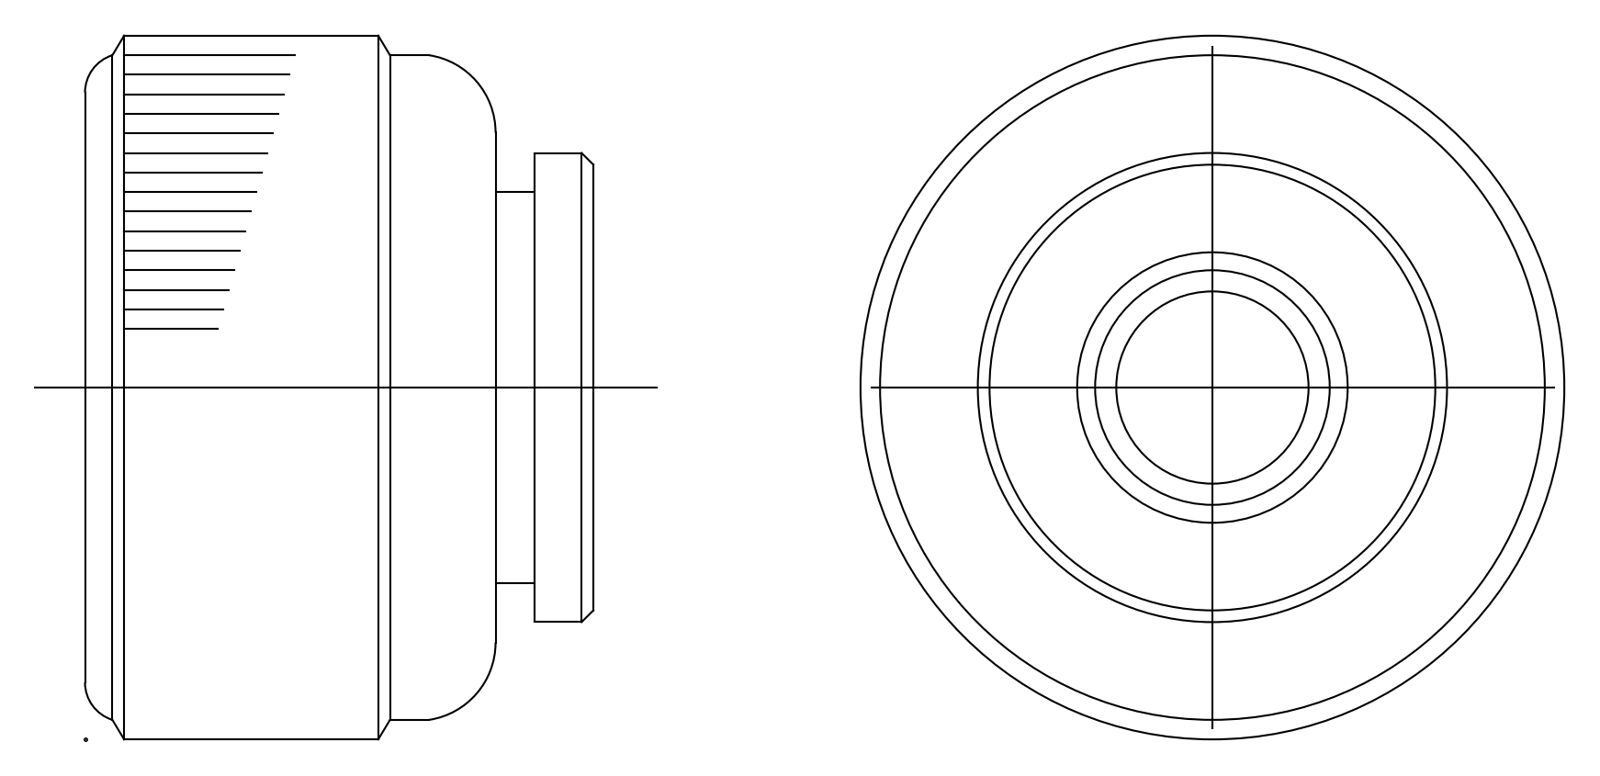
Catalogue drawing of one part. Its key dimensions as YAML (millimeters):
step_written_by: "spGate 20.6.3 (****-****-****-****) (AUTOMOTIVE_DESIGN)"
units: millimeters
bodies: {solids: 1, faces: 32, planar: 4, cylindrical: 12, other: 16}
overall_size: [18, 18, 13]
volume: 2490
surface_area: 1325
round_holes:
  - {diameter: 4.65, count: 1}
  - {diameter: 6, count: 1}
round_bosses_or_shafts:
  - {diameter: 18, count: 1}
  - {diameter: 17, count: 1}
  - {diameter: 12, count: 1}
  - {diameter: 10, count: 1}
face_to_face_distances: [13, 10.5, 2.5, 11.5, 1, 1.5]
